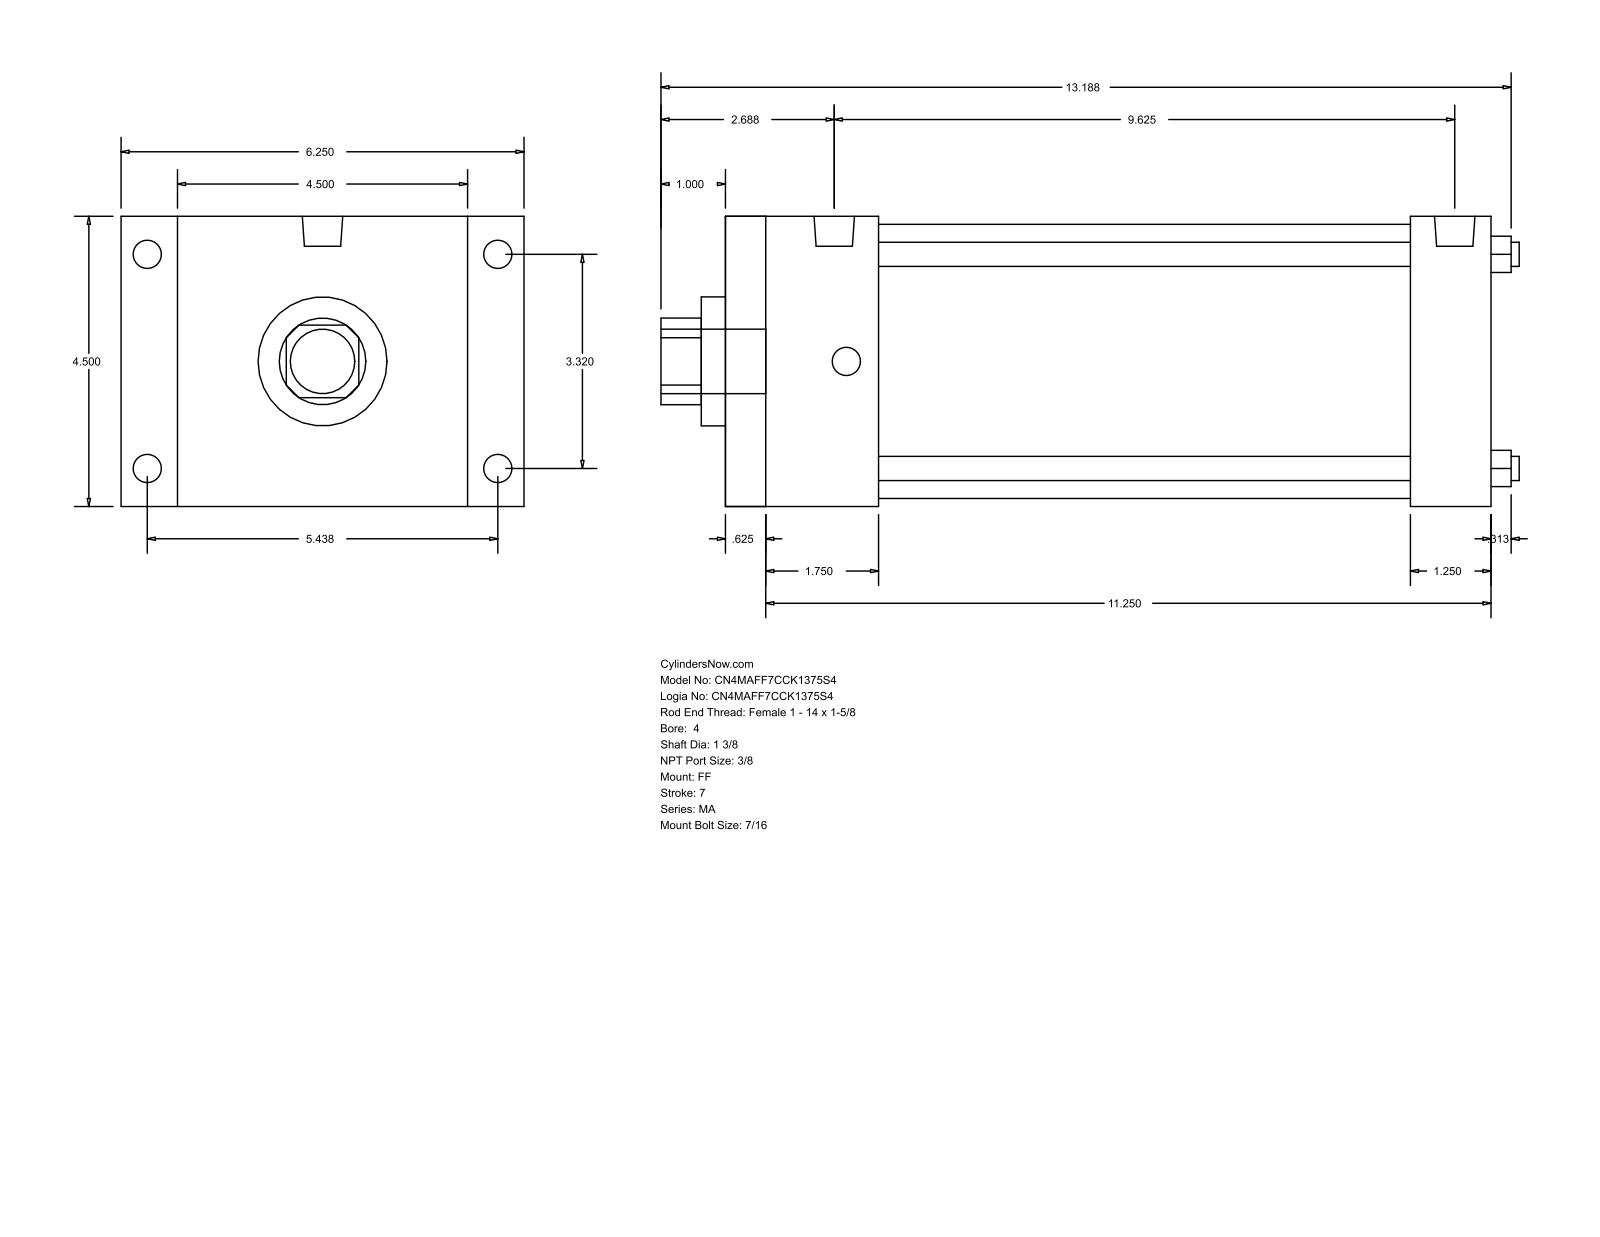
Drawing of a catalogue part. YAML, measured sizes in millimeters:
part_name: "MA_FF__0400_1.375"
step_written_by: "GSSL Pune (CONFIG_CONTROL_DESIGN)"
units: millimeters
bodies: {solids: 0, faces: 92, planar: 64, cylindrical: 28, other: 0}
overall_size: [338.14, 158.75, 114.3]
round_holes:
  - {diameter: 9.53, count: 4}
  - {diameter: 34.92, count: 1}
  - {diameter: 50.8, count: 1}
  - {diameter: 107.95, count: 1}
round_bosses_or_shafts:
  - {diameter: 11.11, count: 8}
  - {diameter: 15.93, count: 2}
  - {diameter: 25.4, count: 1}
partial_cylinders:
  - {radius: 17.06, count: 1}
face_to_face_distances: [114.3, 301.62, 15.87, 285.75, 22.23, 136.53, 269.87, 254, 31.75, 60.32]
hole_center_spacings: [59.62, 84.32, 119.25]
